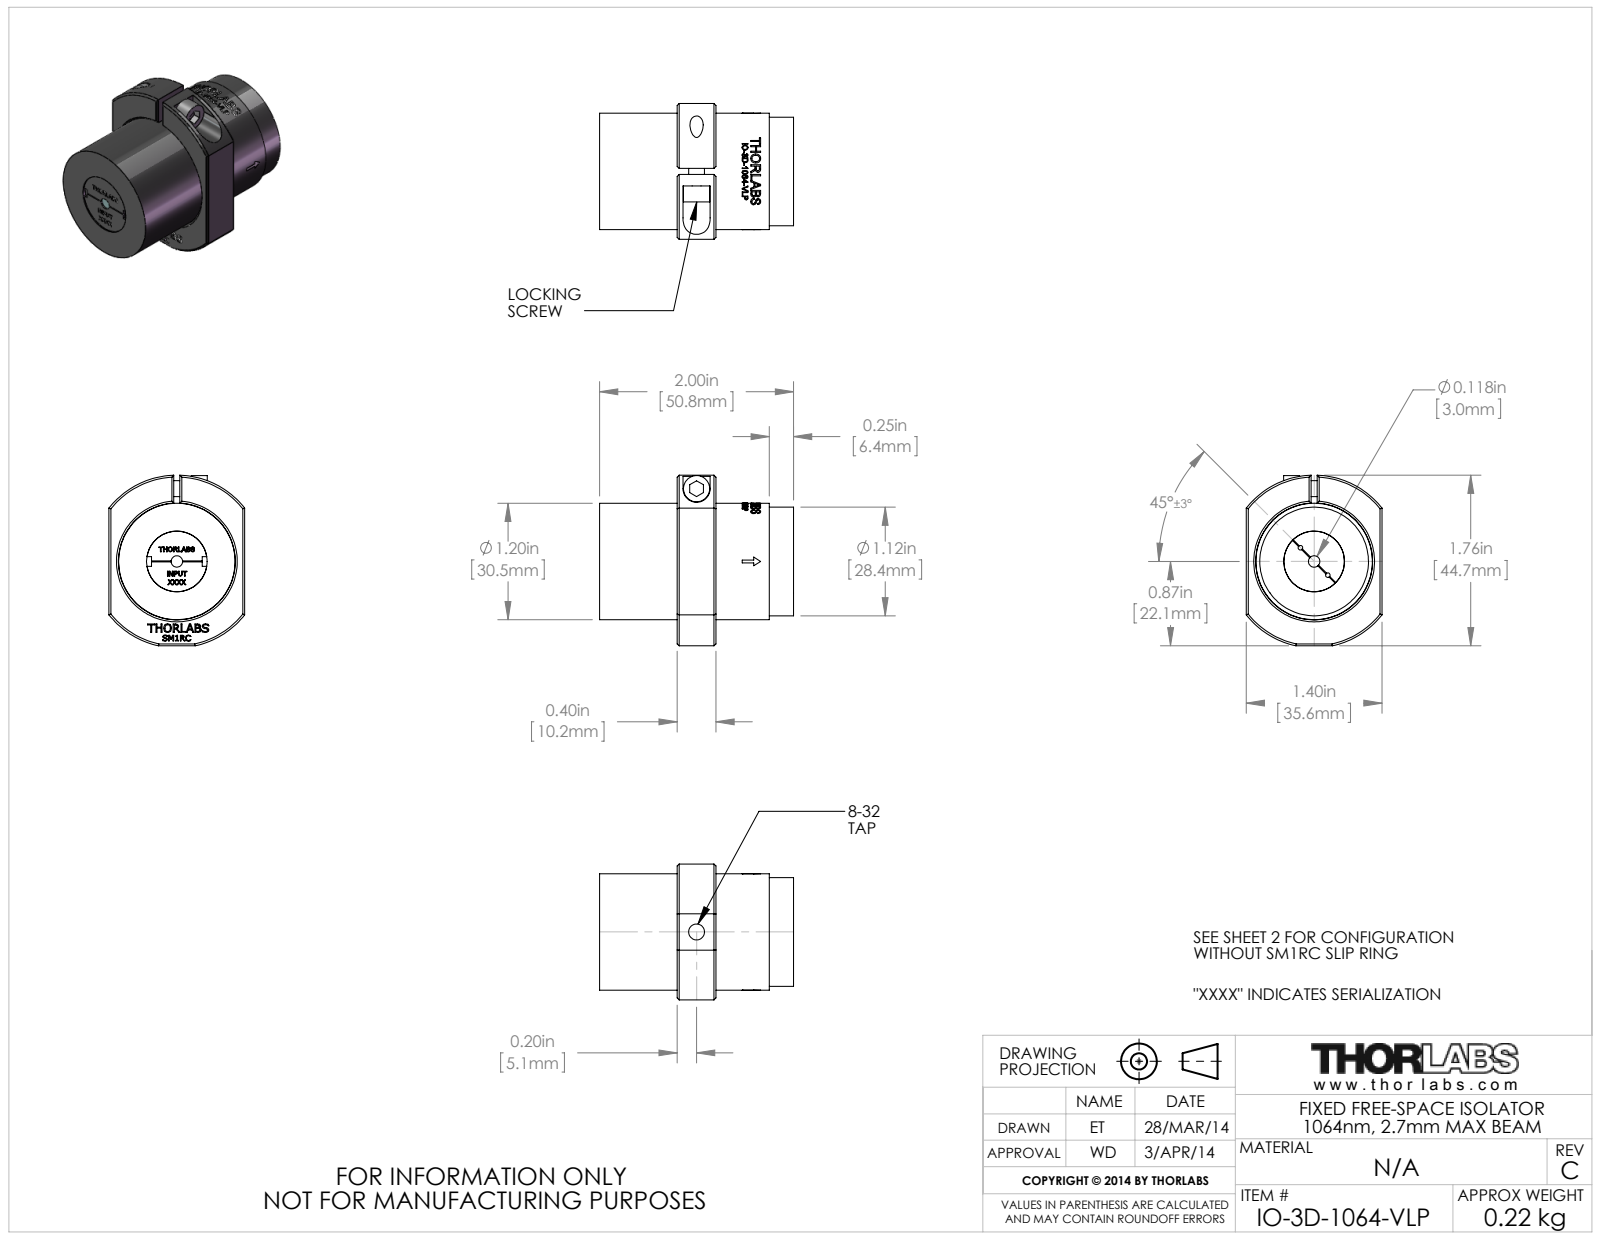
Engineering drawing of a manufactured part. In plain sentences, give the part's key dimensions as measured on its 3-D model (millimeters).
The part is named "17314-E0W". Its 3-D file was written by "SolidWorks 2014 (AUTOMOTIVE_DESIGN)". It is 0 solids with 301 faces: 155 planar, 72 cylindrical and 74 other. Overall it measures 50.8 by 44.69 by 35.56 millimeters. Round holes: 2 of diameter 1.19, 2 of diameter 4.17, 1 of diameter 3, 1 of diameter 3.45, 1 of diameter 4.57, 1 of diameter 15.88, 1 of diameter 30.61. Round bosses or shafts: 1 of diameter 30.48, 1 of diameter 28.45, 1 of diameter 6.86. Partial cylindrical surfaces (rounded edges, fillets, slot ends): 1 of radius 3.56, 1 of radius 22.61. The main face-to-face distances are 20.32, 30.48, 10.16, 50.8, 35.56, 19.56, 13.97, 0.76, 29.72, 50.04. The hole center spacings are 5.08, 10.15.
